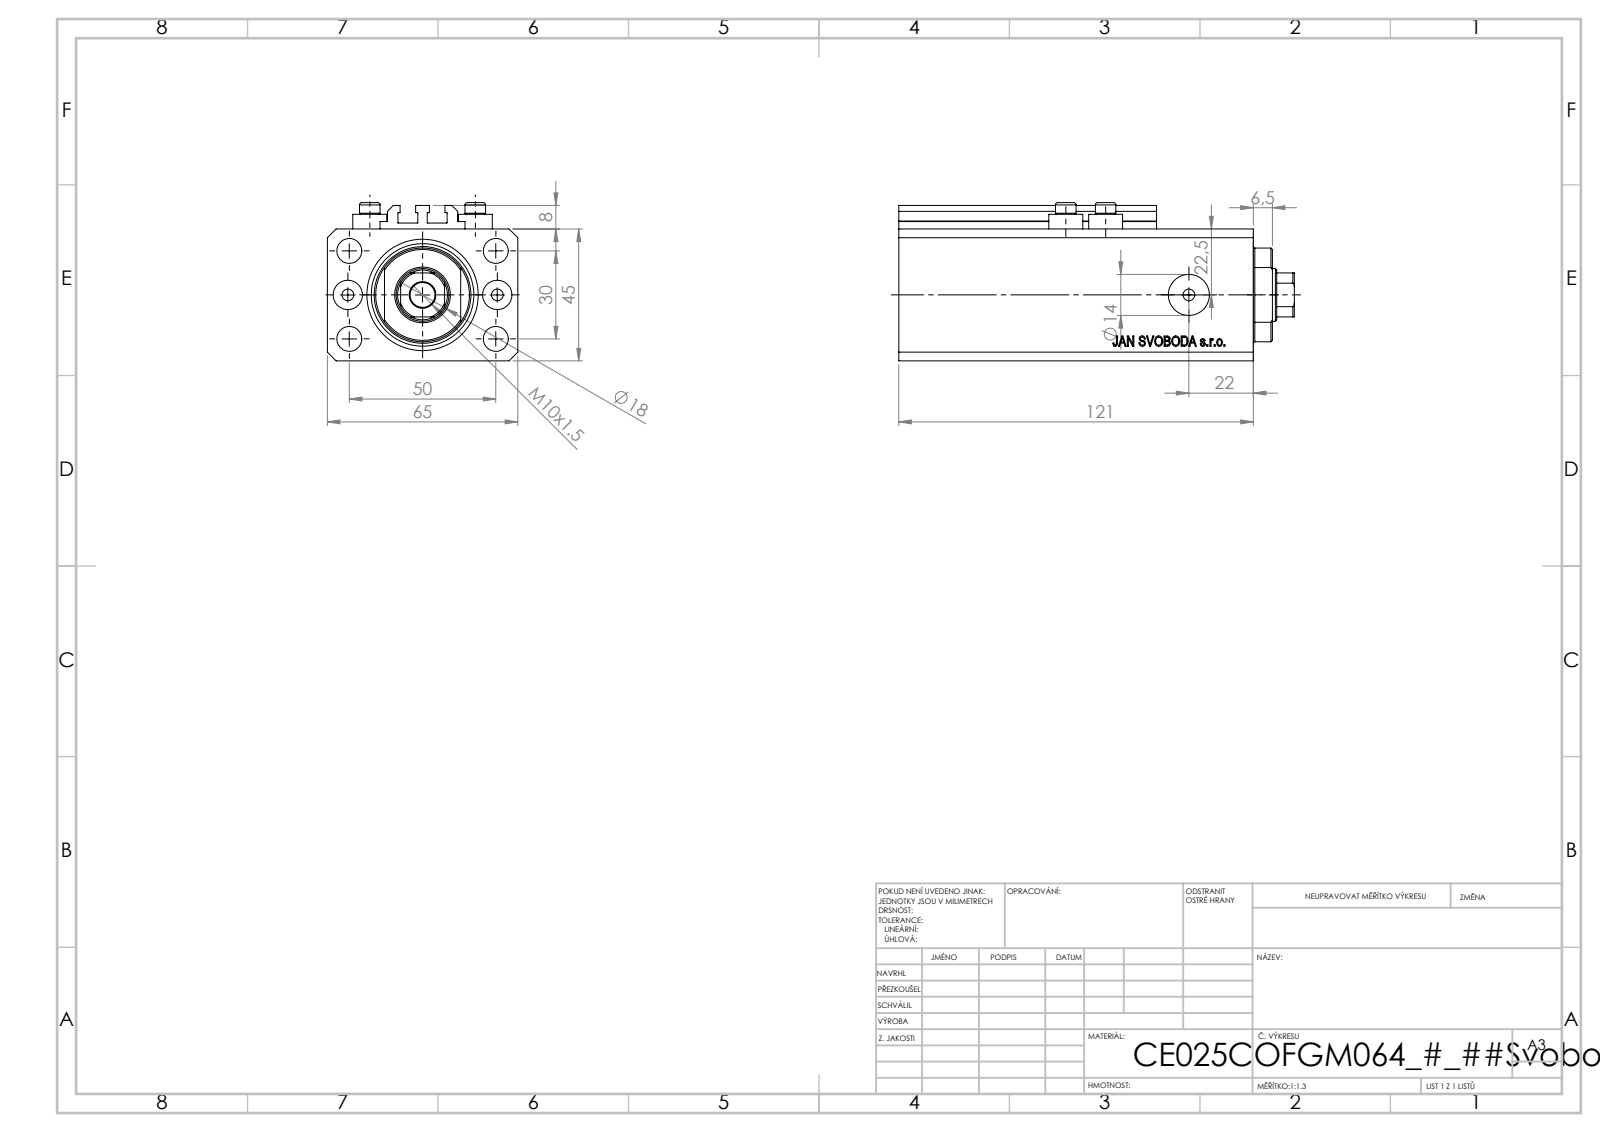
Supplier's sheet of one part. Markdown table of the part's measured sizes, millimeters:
| quantity | value |
| --- | --- |
| part name | V250CE_VC_C; V250CE_C_Body; V250CE_C_VCP; ALLEN BOLT V250CE |
| STEP written by | SolidWorks 2019 (CONFIG_CONTROL_DESIGN) |
| units | millimeters |
| bodies | 8 solids, 1034 faces (504 planar, 86 cylindrical, 444 other) |
| overall size | 135 × 65 × 54 |
| volume | 325 010 mm³ |
| surface area | 81 715 mm² |
| round holes (diameter × count) | 4 × 8, 8.5 × 5, 10 × 2, 14 × 2, 18 × 1, 25 × 1, 38 × 1 |
| round bosses / shafts (diameter × count) | 11.6 × 4, 7 × 4 |
| partial cylindrical surfaces (radius × count) | 0.2 × 10, 8.5 × 1, 16 × 1 |
| main face-to-face distances | 45, 65, 14, 47, 107, 121, 2.5, 10, 2, 20.5 |
| hole center spacings | 15.01, 29.15, 52.68, 13.6, 25.5, 30, 36, 38.48 |
